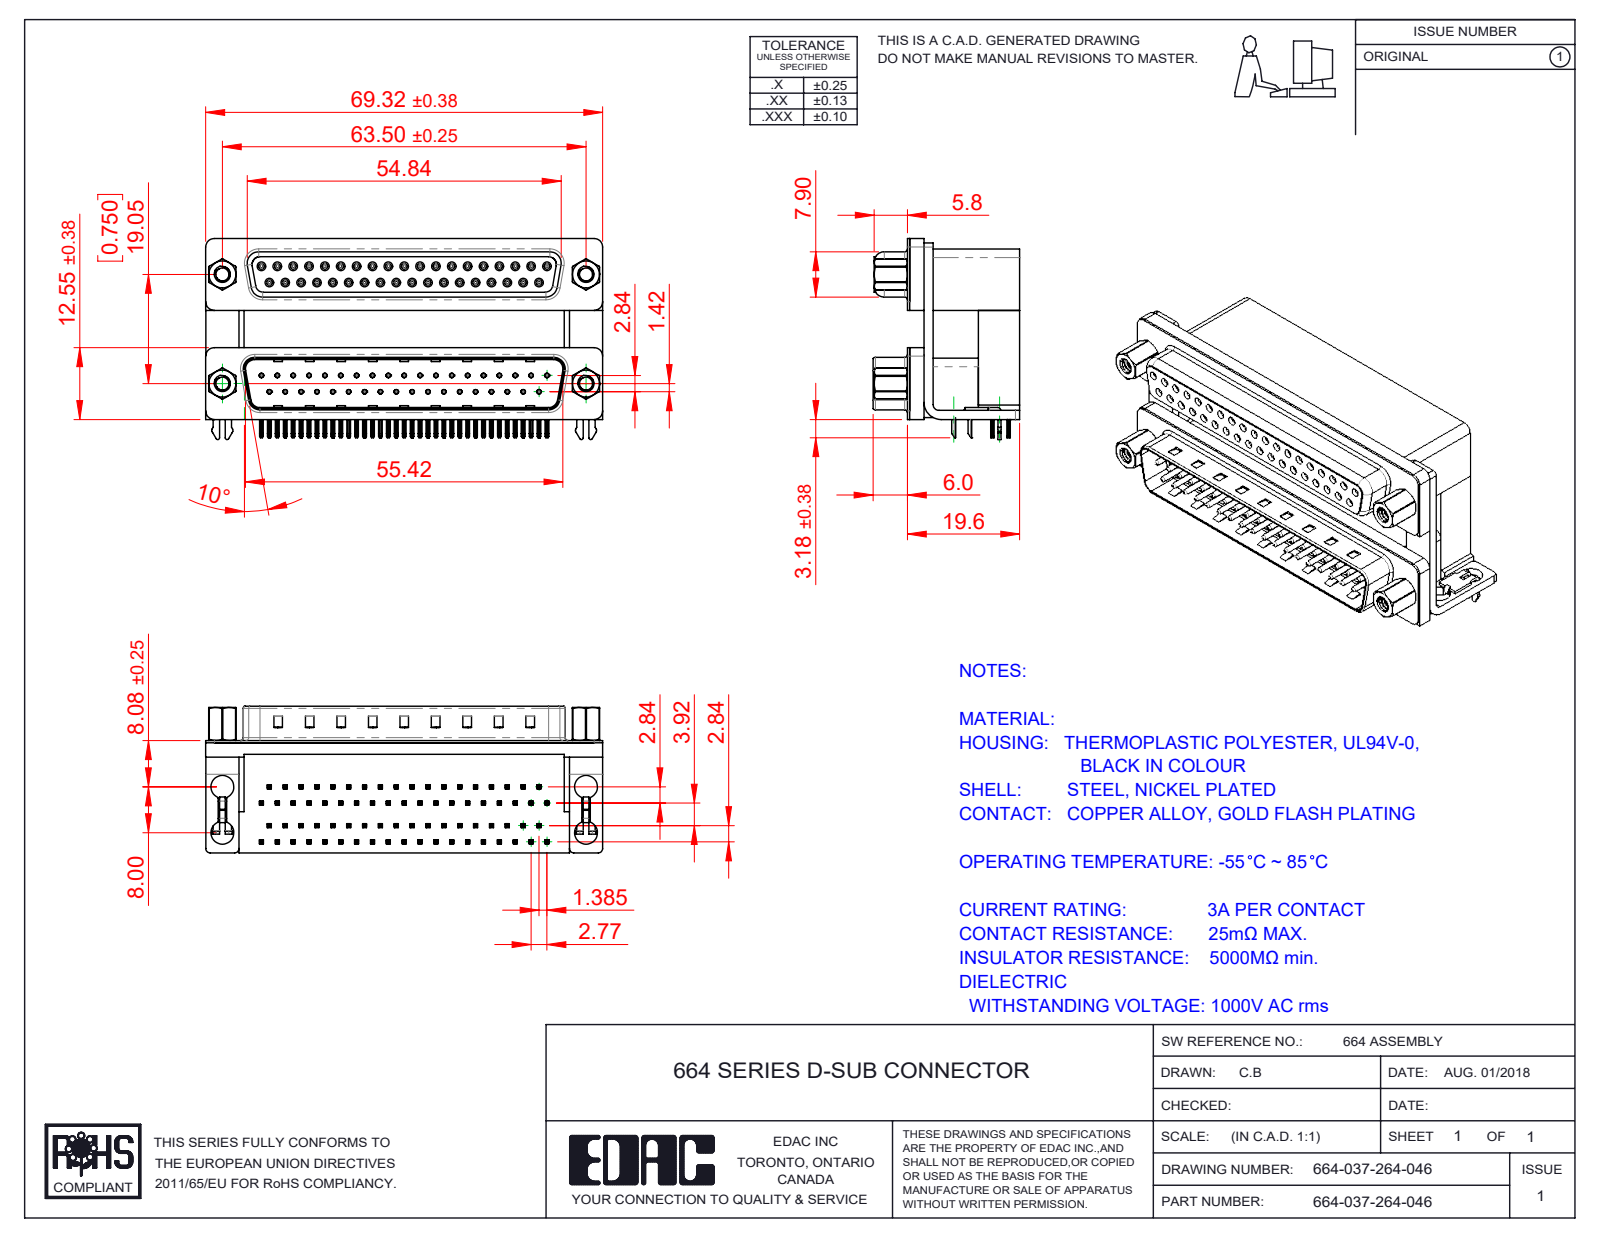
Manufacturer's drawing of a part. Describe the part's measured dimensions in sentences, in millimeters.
The part is named "664 Mounting Bracket_2ProngM; 664 Contact Bottom Upper_M; 664 Contact Bottom Lower; 664 Housing Upper_37 Contacts M (+8 more)". Its 3-D file was written by "SolidWorks 2020 (CONFIG_CONTROL_DESIGN)". It is 91 solids with 9305 faces: 4863 planar, 2351 cylindrical and 2091 other. Overall it measures 69.32 by 35.1 by 25.6 millimeters. Its volume is 31 524 cubic millimeters and its surface area 33 770 square millimeters. Round holes: 74 of diameter 0.8, 37 of diameter 0.35, 37 of diameter 0.9, 8 of diameter 4, 4 of diameter 2.26, 4 of diameter 2.29, 4 of diameter 3.5, 4 of diameter 4.8, 4 of diameter 5. Round bosses or shafts: 37 of diameter 1.2, 37 of diameter 0.75, 4 of diameter 4.9, 4 of diameter 4.75, 4 of diameter 3.9, 4 of diameter 2.79. Partial cylindrical surfaces (rounded edges, fillets, slot ends): 297 of radius 0.1, 154 of radius 0.25, 148 of radius 0.15, 74 of radius 0.12, 74 of radius 0.35, 37 of radius 0.34, 18 of radius 0.28, 16 of radius 0.5. The main face-to-face distances are 0.4, 19.2, 7.2, 12, 10.69, 2.19, 2.84, 18.7, 29.39, 19.05. The hole center spacings are 2.77, 5.54, 3.16, 8.31, 11.08, 13.85, 16.62, 19.39.
